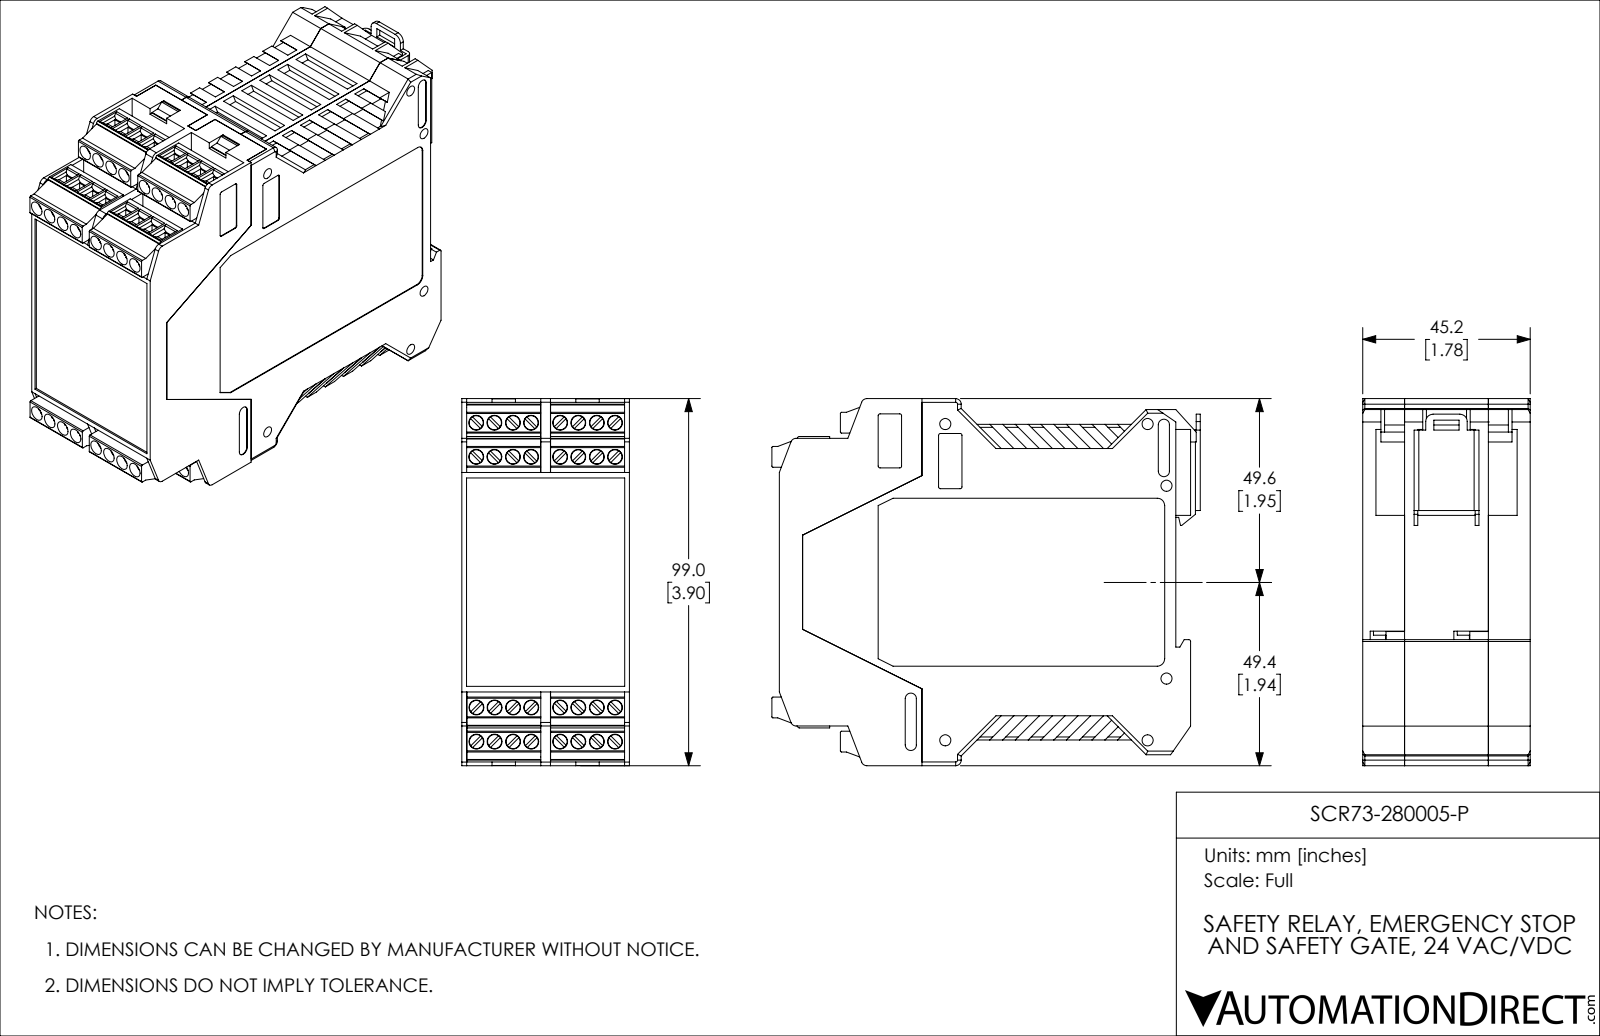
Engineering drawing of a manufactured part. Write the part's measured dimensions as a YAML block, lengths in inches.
part_name: "SCR73-280005-P"
step_written_by: "SolidWorks 2019 (AUTOMOTIVE_DESIGN)"
units: inches
bodies: {solids: 25, faces: 4329, planar: 3489, cylindrical: 786, other: 54}
overall_size: [4.551, 3.898, 1.78]
volume: 6.741
surface_area: 188.8
round_holes:
  - {diameter: 0.157, count: 32}
  - {diameter: 0.118, count: 8}
  - {diameter: 0.079, count: 2}
round_bosses_or_shafts:
  - {diameter: 0.15, count: 32}
  - {diameter: 0.11, count: 16}
  - {diameter: 0.055, count: 16}
partial_cylinders:
  - {radius: 0.008, count: 154}
  - {radius: 0.047, count: 44}
  - {radius: 0.02, count: 21}
  - {radius: 0.012, count: 20}
  - {radius: 0.115, count: 16}
  - {radius: 0.01, count: 12}
  - {radius: 0.059, count: 10}
  - {radius: 0.079, count: 4}
face_to_face_distances: [1.72, 0.059, 0.051, 1.772, 1.713, 1.661, 0.394, 1.78, 0.89, 1.728]
hole_center_spacings: [0.39, 3.03, 0.193, 0.362, 0.41, 0.532, 3.024, 3.049]
